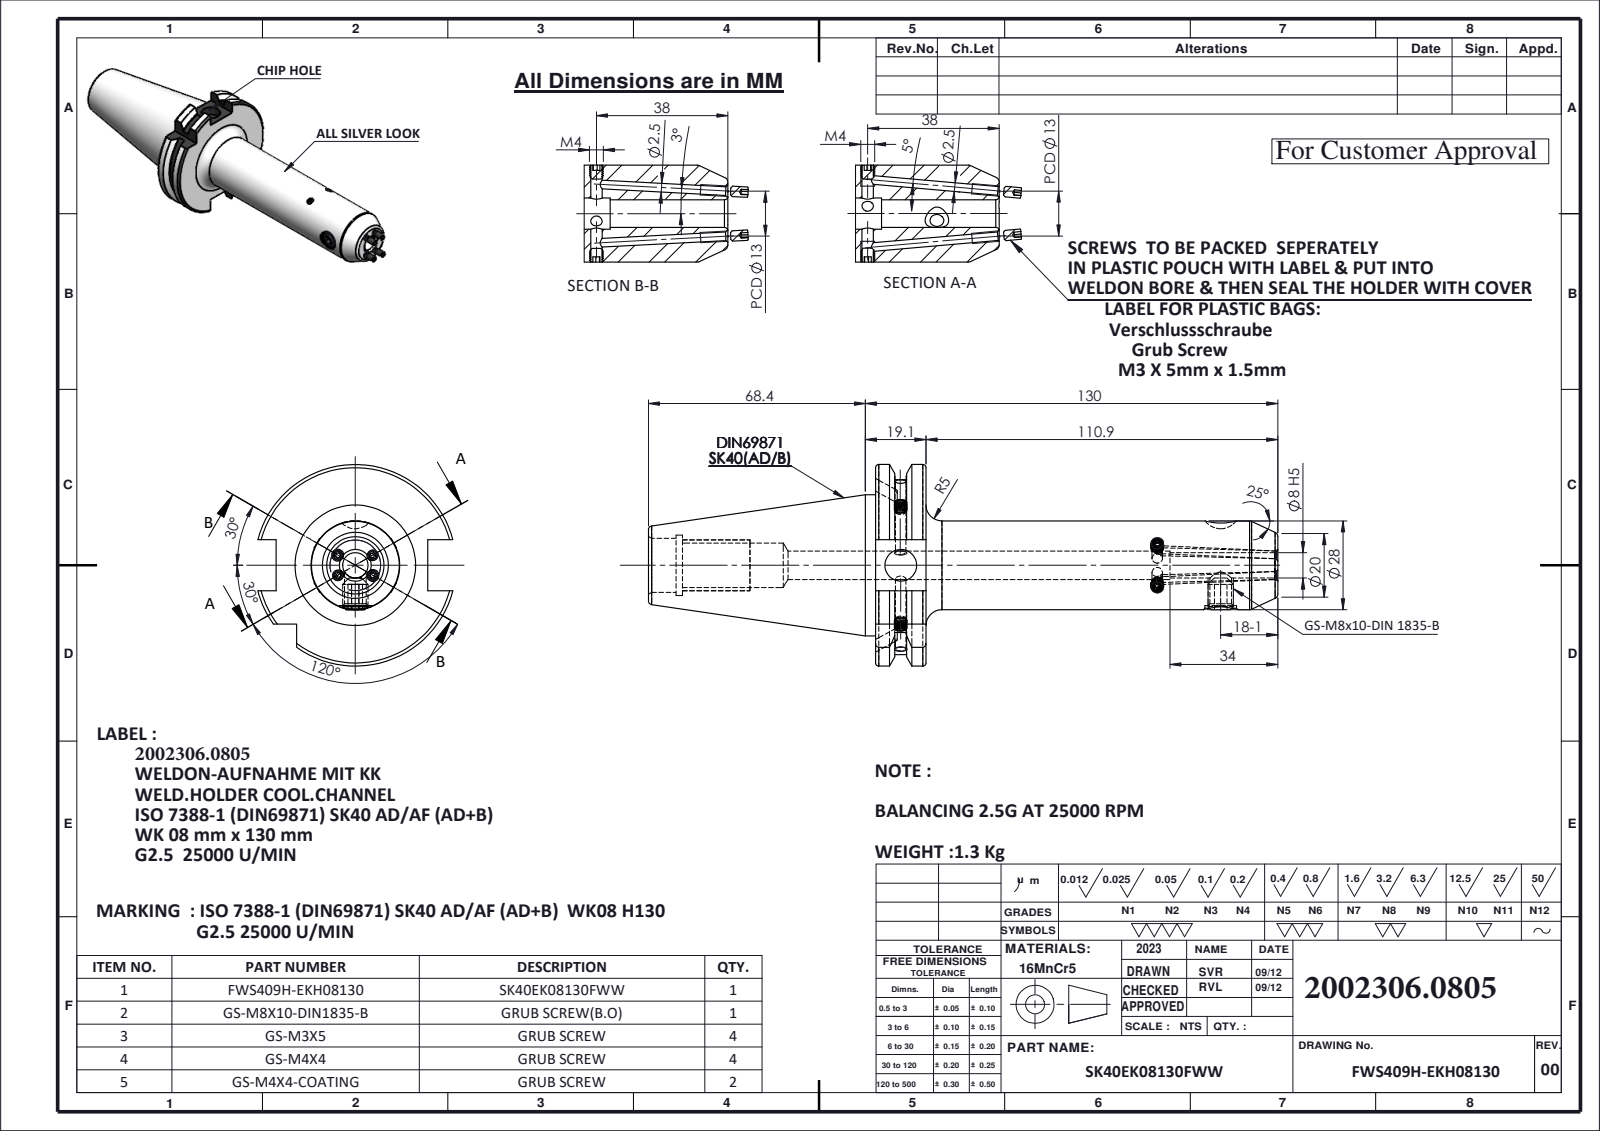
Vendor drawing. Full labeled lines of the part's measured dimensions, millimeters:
Part name (STEP PRODUCT): GS-M3X5; GS-M4X4_DIN 913 - M4 x 4-N; GS-M4X4-COATING_DIN 913 - M4 x 4-N; SK40EK08130FWW (+2 more)
STEP written by: SolidWorks 2023 (CONFIG_CONTROL_DESIGN)
Units: millimetres
Bodies: 12 solids, 519 faces (149 planar, 122 cylindrical, 248 other)
Overall size (bounding box): 204.84 × 63.55 × 61.48
Volume: 162 181 mm³ · Surface area: 35 880 mm²
Round holes (diameter × count): ⌀2.5 ×4, ⌀3.3 ×3, ⌀10 ×2, ⌀6.8 ×1, ⌀8 ×1, ⌀9 ×1, ⌀14 ×1, ⌀17 ×1, ⌀19 ×1
Round bosses / shafts (diameter × count): ⌀4 ×5, ⌀3 ×4, ⌀44.45 ×1, ⌀28 ×1, ⌀8 ×1
Partial cylindrical surfaces — rounded edges, fillets, slot ends (radius × count): R28.12 ×1, R31.77 ×1
Main face-to-face distances: 15.9, 16.1, 47.8, 126.8, 110.9, 71.6, 87.5, 198.4, 10.7, 60.9
